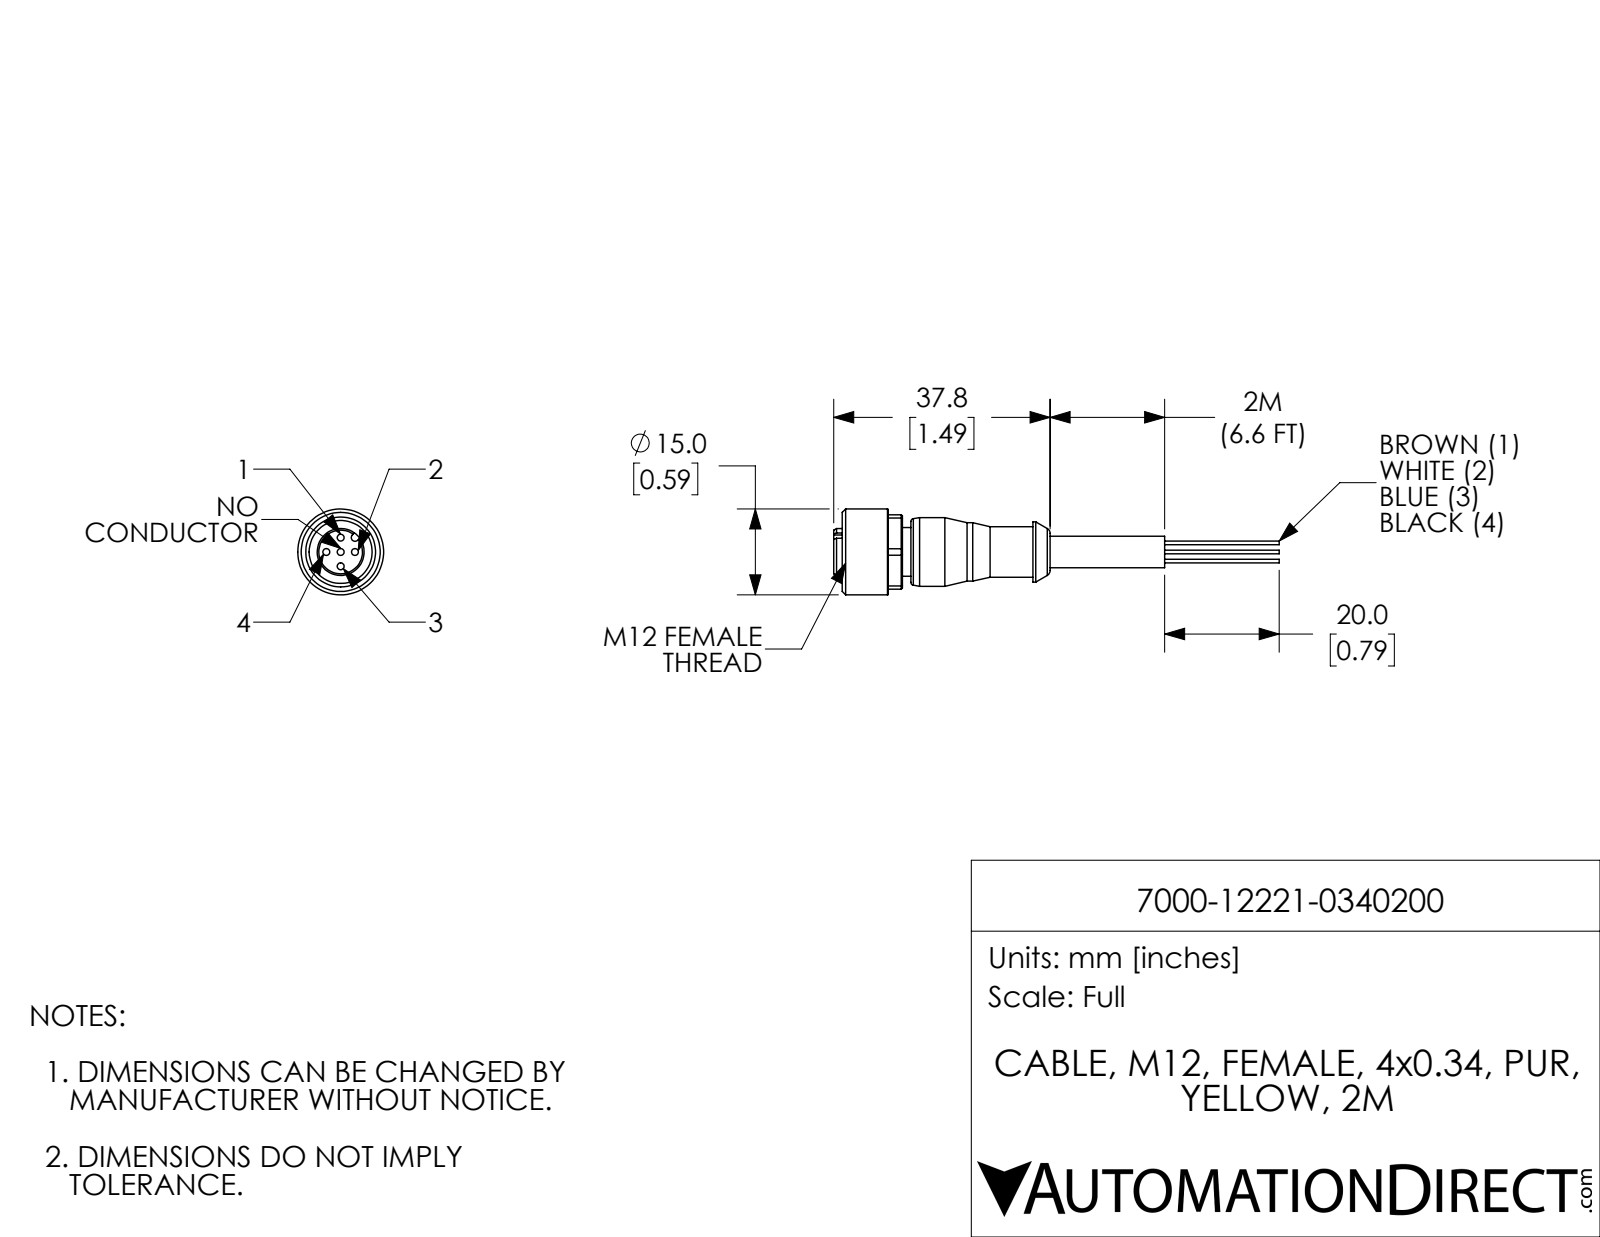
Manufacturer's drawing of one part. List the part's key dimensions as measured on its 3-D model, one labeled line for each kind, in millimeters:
Part name (STEP PRODUCT): 7000-12221-0340200
STEP written by: SolidWorks 2021 (CONFIG_CONTROL_DESIGN)
Units: millimetres
Bodies: 1 solid, 103 faces (33 planar, 43 cylindrical, 27 other)
Overall size (bounding box): 77.8 × 15 × 15
Volume: 4 050 mm³ · Surface area: 2 830 mm²
Round holes (diameter × count): ⌀1.2 ×5, ⌀11 ×1
Round bosses / shafts (diameter × count): ⌀0.7 ×4, ⌀15 ×1, ⌀12 ×1, ⌀10.5 ×1, ⌀10.2 ×1, ⌀8.8 ×1, ⌀8.5 ×1, ⌀8.2 ×1
Partial cylindrical surfaces — rounded edges, fillets, slot ends (radius × count): R0.7 ×1, R7.2 ×1
Main face-to-face distances: 12, 1.5, 3, 13, 9, 25.8, 7.5, 10.5, 2.5, 13.5
Hole centre spacings: 2.5, 3.5, 5
